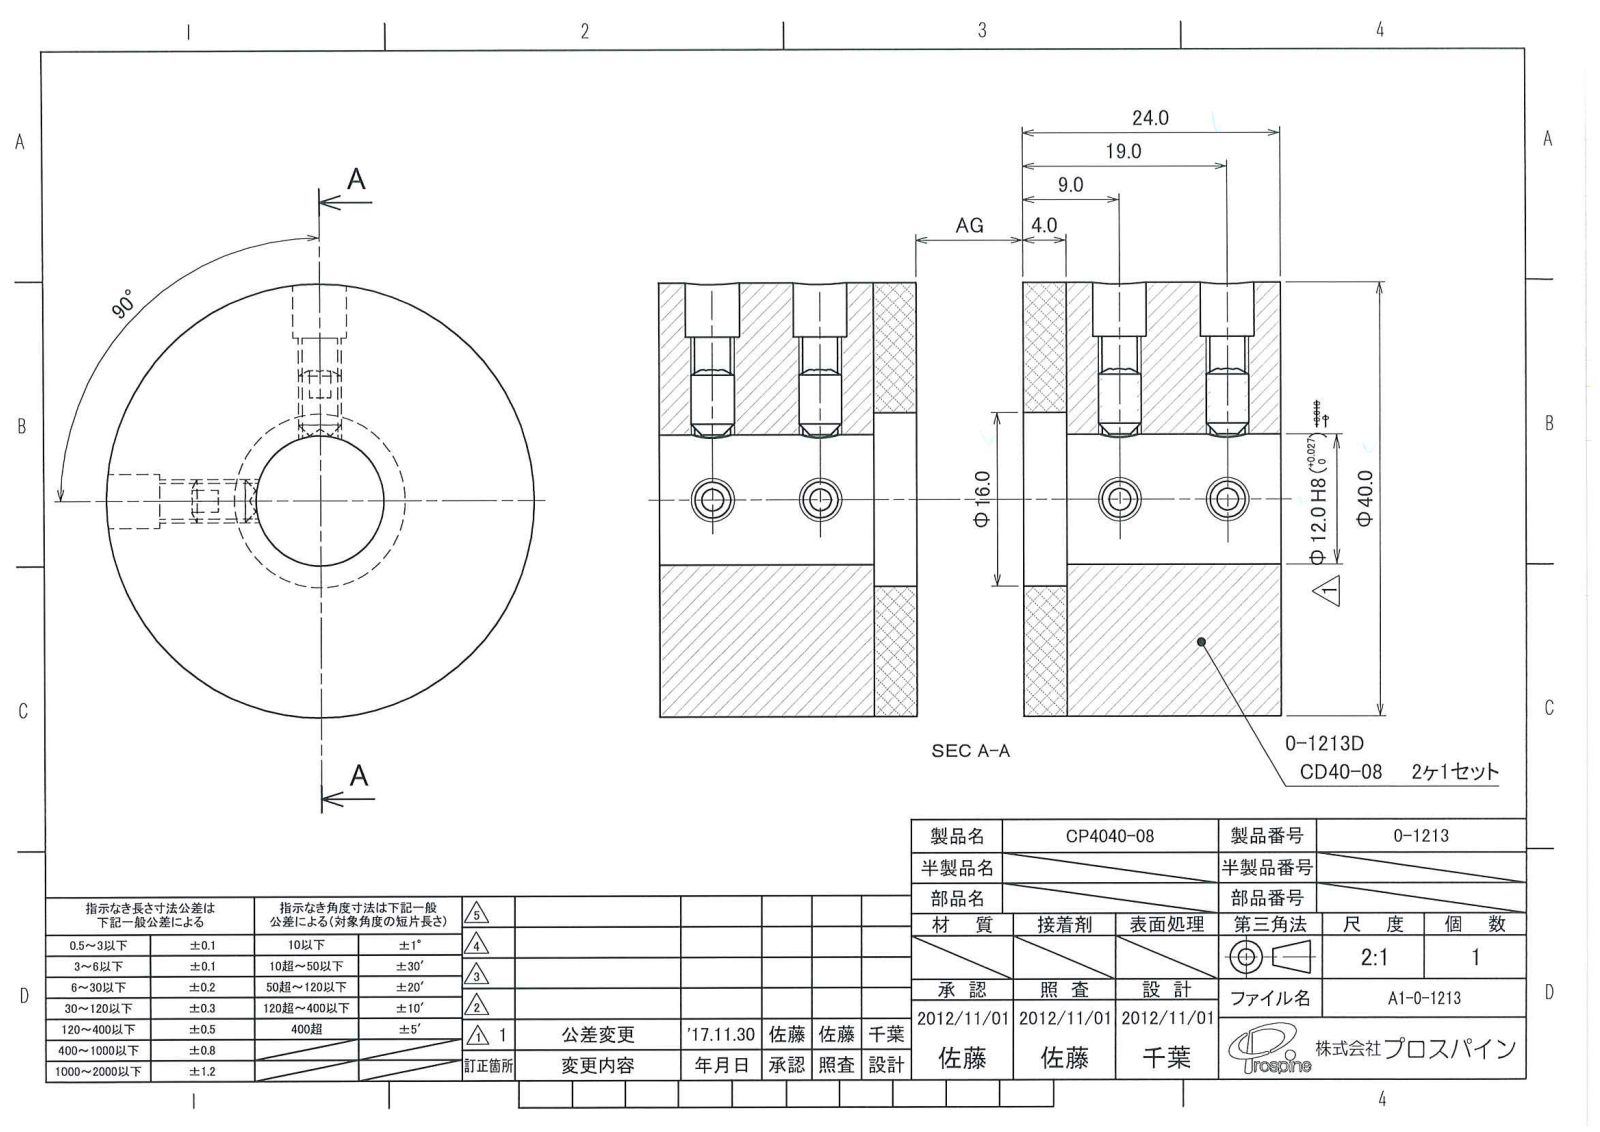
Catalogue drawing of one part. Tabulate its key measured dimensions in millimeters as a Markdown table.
| quantity | value |
| --- | --- |
| STEP written by | PSStep 10.0 (CONFIG_CONTROL_DESIGN) |
| units | millimeters |
| bodies | 8 solids, 86 faces (50 planar, 18 cylindrical, 18 other) |
| overall size | 40 × 40 × 24 |
| volume | 26 743 mm³ |
| surface area | 9 613 mm² |
| round holes (diameter × count) | 3.3 × 4, 5 × 4, 12 × 1, 16 × 1 |
| round bosses / shafts (diameter × count) | 4 × 4, 40 × 1 |
| main face-to-face distances | 20, 24, 4, 2, 8.66, 5.47, 6.66, 10.66, 14, 16 |
| hole center spacings | 10 |
